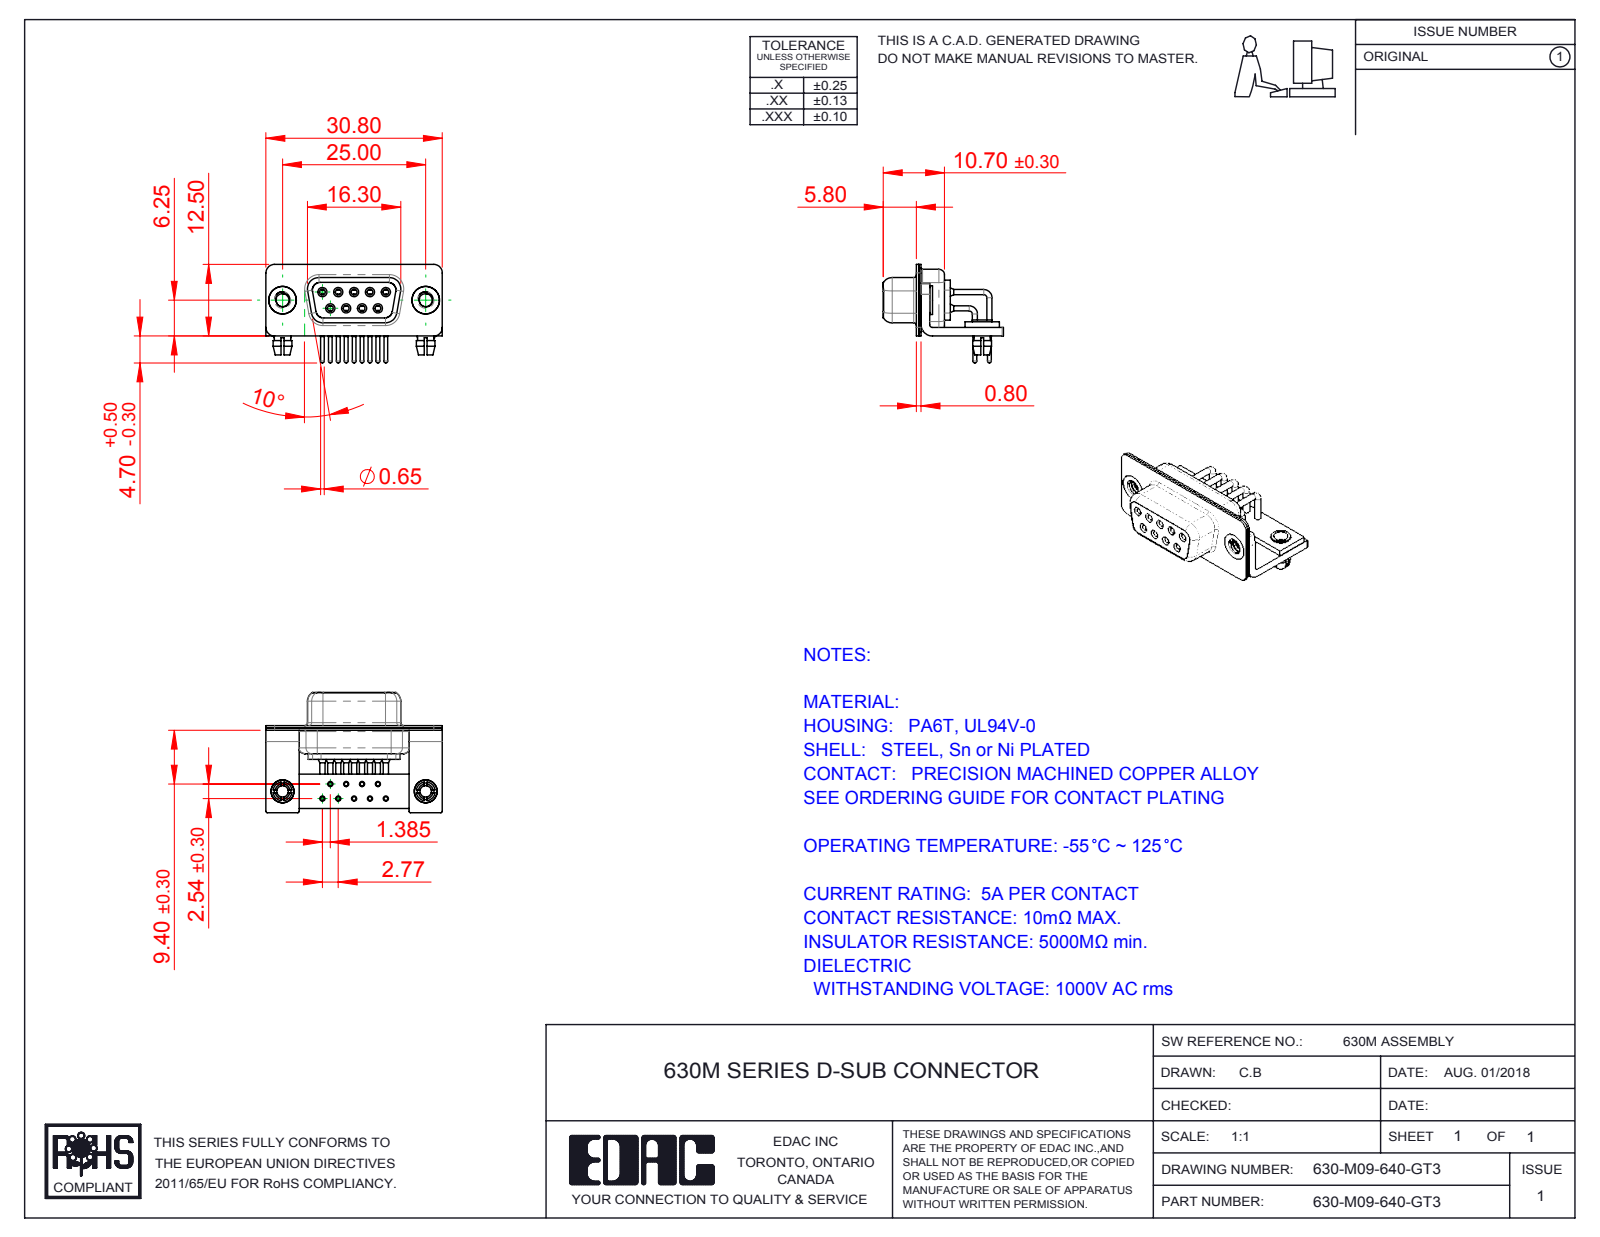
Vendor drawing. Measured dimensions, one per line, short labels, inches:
name: 630M Shell Front_09 Contacts; 630-M09-640-GT3; 630M Contact Row 1; 630M Contact Row 2 (+6 more)
written by: SolidWorks 2016 (CONFIG_CONTROL_DESIGN)
unit: in
bodies: 19 solids, 916 faces (276 planar, 416 cylindrical, 224 other)
size: 1.213 × 0.827 × 0.677
volume: 0.137 in³; area: 9.171 in²
holes: 11× ⌀0.079, 9× ⌀0.035, 9× ⌀0.039, 9× ⌀0.043, 9× ⌀0.067, 9× ⌀0.071, 2× ⌀0.089, 2× ⌀0.098, 2× ⌀0.126, 2× ⌀0.157, 2× ⌀0.189
bosses: 9× ⌀0.063, 9× ⌀0.059, 9× ⌀0.035, 9× ⌀0.026, 2× ⌀0.197, 2× ⌀0.193, 2× ⌀0.157, 2× ⌀0.134
rounds: 16× R0.01, 16× R0.059, 13× R0.079, 8× R0.053, 8× R0.063, 5× R0.02, 4× R0.024, 4× R0.026
face distances: 0.016, 0.031, 0.059, 0.091, 0.075, 0.039, 0.368, 0.057, 0.098, 0.352
hole spacings: 0.109, 0.218, 0.124, 0.192, 0.327, 0.114, 0.114, 0.198
